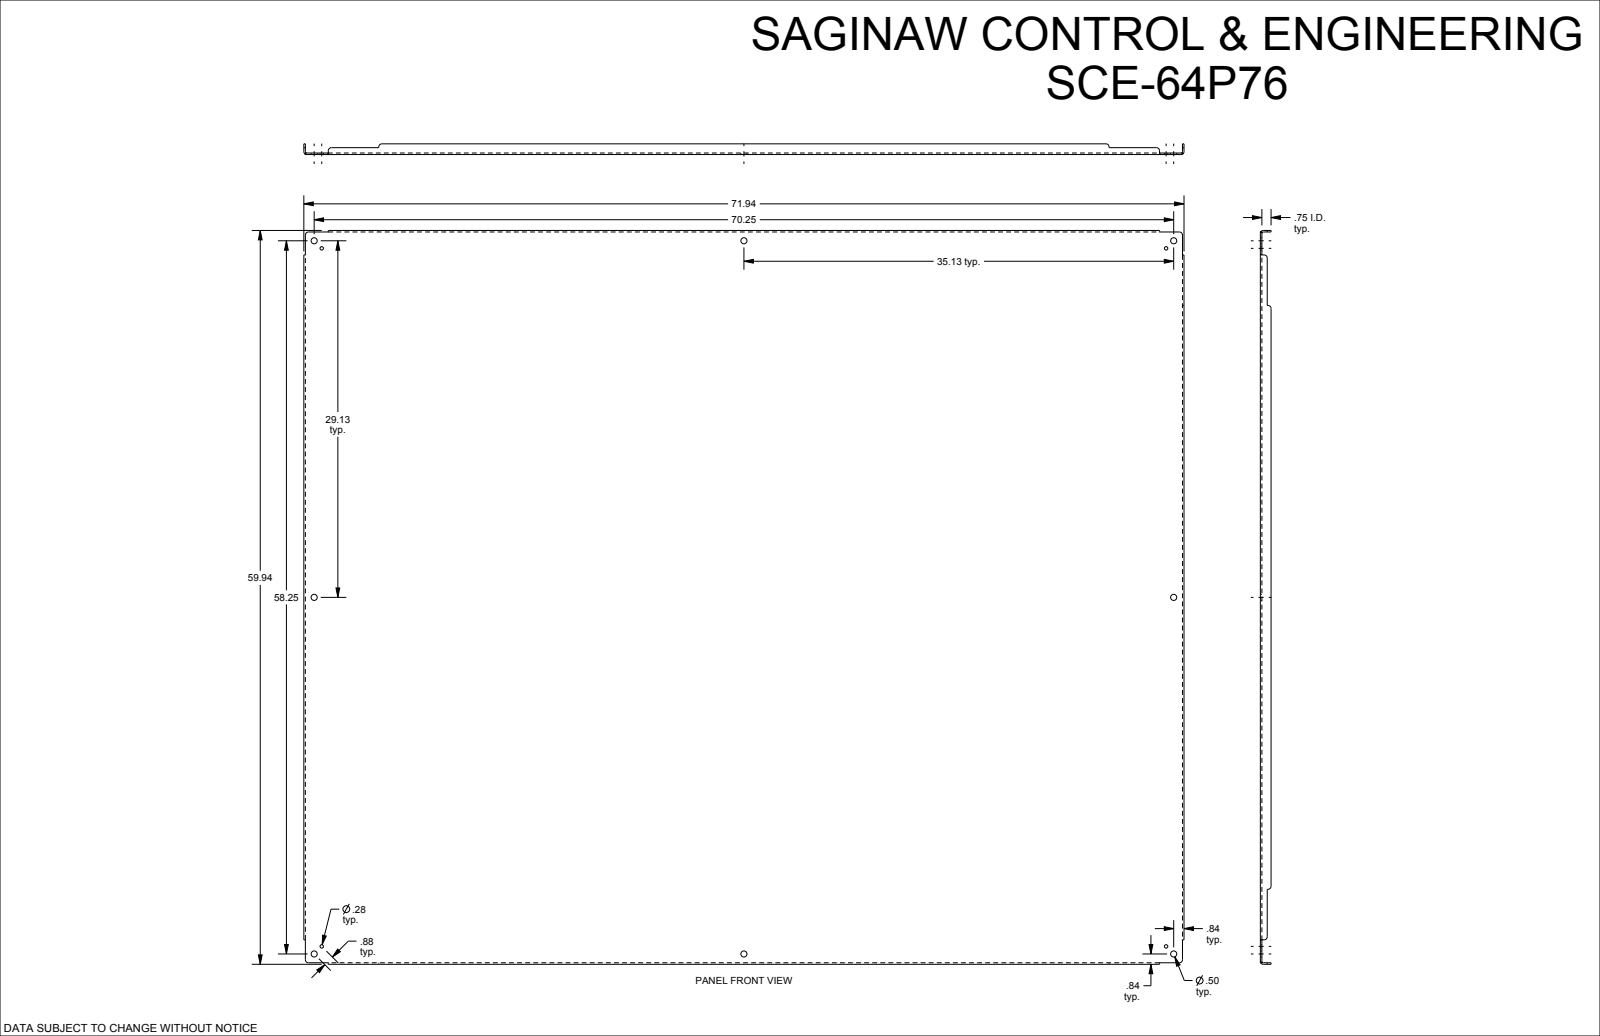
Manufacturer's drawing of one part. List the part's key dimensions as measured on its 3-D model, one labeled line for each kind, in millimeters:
Part name (STEP PRODUCT): SCE-64P76
STEP written by: SolidWorks 2019 (CONFIG_CONTROL_DESIGN)
Units: millimetres
Bodies: 1 solid, 110 faces (46 planar, 40 cylindrical, 24 other)
Overall size (bounding box): 1827.2 × 1522.4 × 22.2
Volume: 9 146 000 mm³ · Surface area: 5 784 000 mm²
Round holes (diameter × count): ⌀12.7 ×8, ⌀7.1 ×4
Partial cylindrical surfaces — rounded edges, fillets, slot ends (radius × count): R6.4 ×12, R2.8 ×4, R6 ×4
Main face-to-face distances: 3.2, 3.2, 1519.3, 1824.1, 1516, 1522.4, 1820.8, 1827.2, 19.1, 22.2
Hole centre spacings: 22.2, 724.2, 739.8, 876.6, 892.2, 1159, 1463.9, 1706.2
